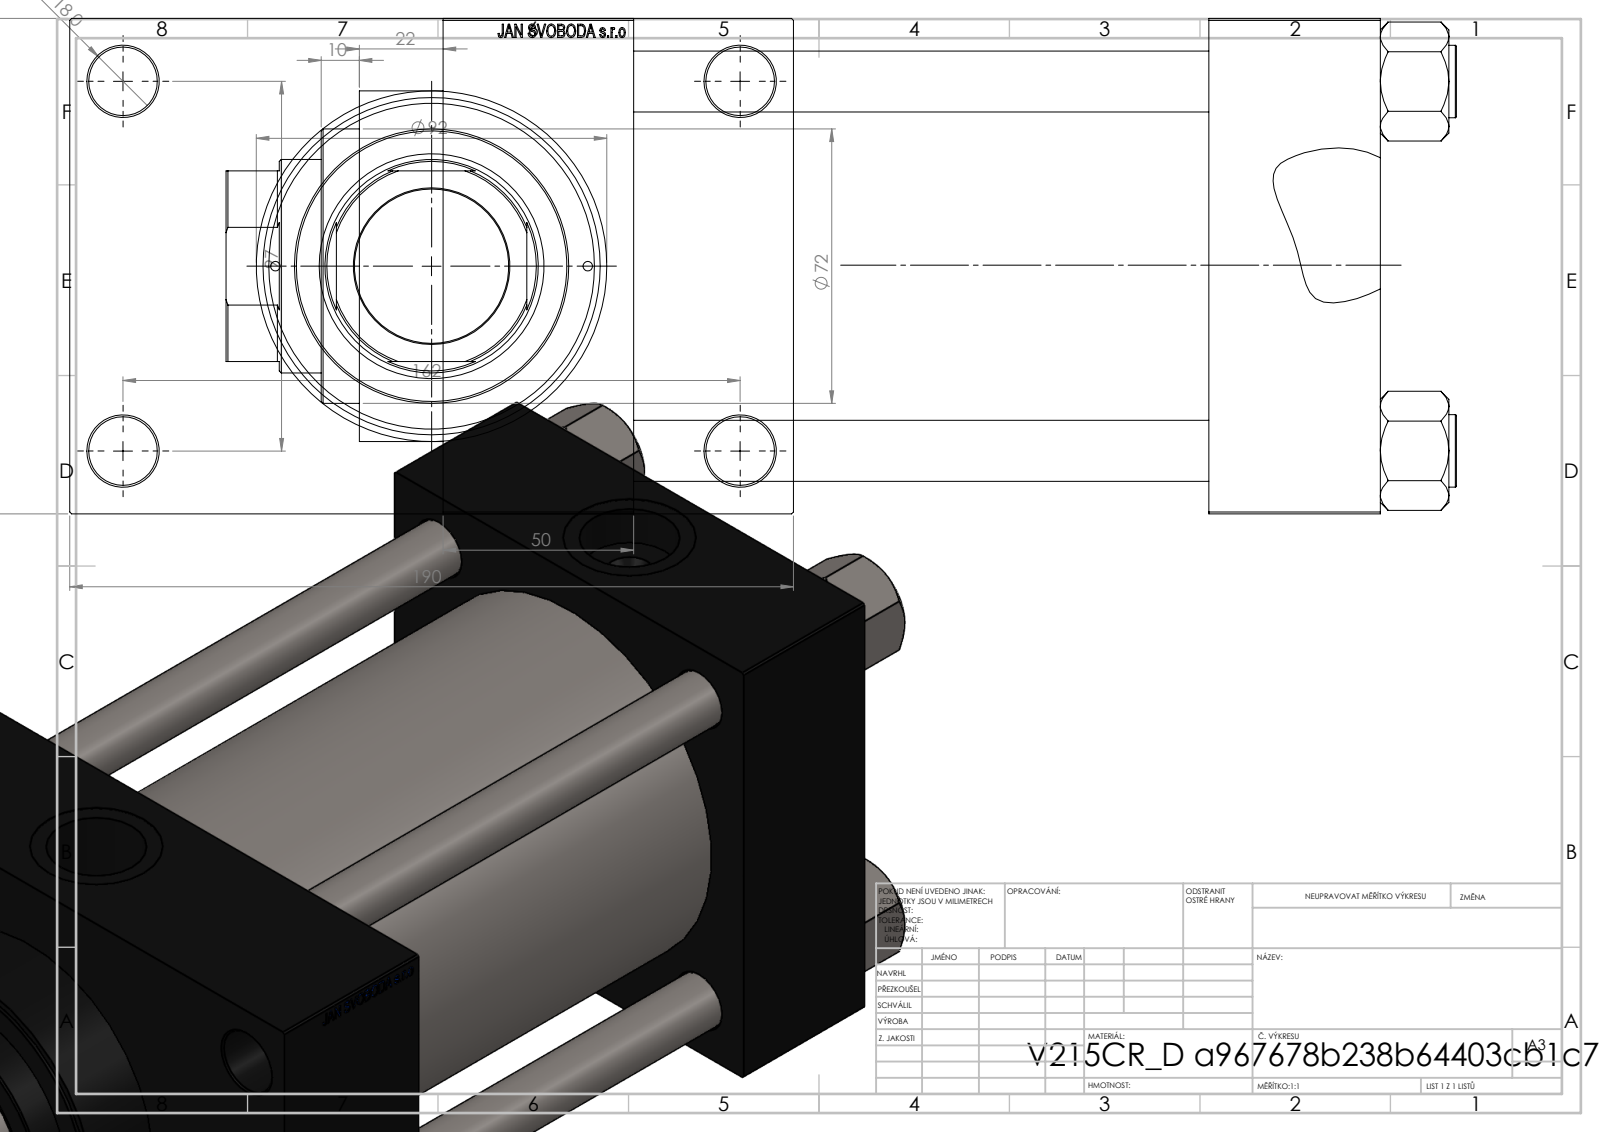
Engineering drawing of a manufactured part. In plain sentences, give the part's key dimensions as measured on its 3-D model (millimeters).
The part is named "V215_VC_A; V215CR_VCP_D; V215CR_D_Body; NUT_M5_D (+1 more)". Its 3-D file was written by "SolidWorks 2019 (CONFIG_CONTROL_DESIGN)". It is 11 solids with 1160 faces: 547 planar, 93 cylindrical and 520 other. Overall it measures 323 by 190 by 130 millimeters. Its volume is 2 983 000 cubic millimeters and its surface area 441 658 square millimeters. Round holes: 4 of diameter 16, 4 of diameter 18, 2 of diameter 2.5, 2 of diameter 7, 2 of diameter 26.44, 2 of diameter 35, 1 of diameter 40.5, 1 of diameter 56, 1 of diameter 59, 1 of diameter 76, 1 of diameter 85.5, 1 of diameter 100. Round bosses or shafts: 4 of diameter 19, 1 of diameter 106, 1 of diameter 92, 1 of diameter 72. Partial cylindrical surfaces (rounded edges, fillets, slot ends): 1 of radius 27. The main face-to-face distances are 130, 50, 45, 196, 151, 246, 201, 30, 160, 190. The hole center spacings are 32.55, 49.02, 62.87, 68.52, 94.41, 96.9, 101.73, 102.27.
